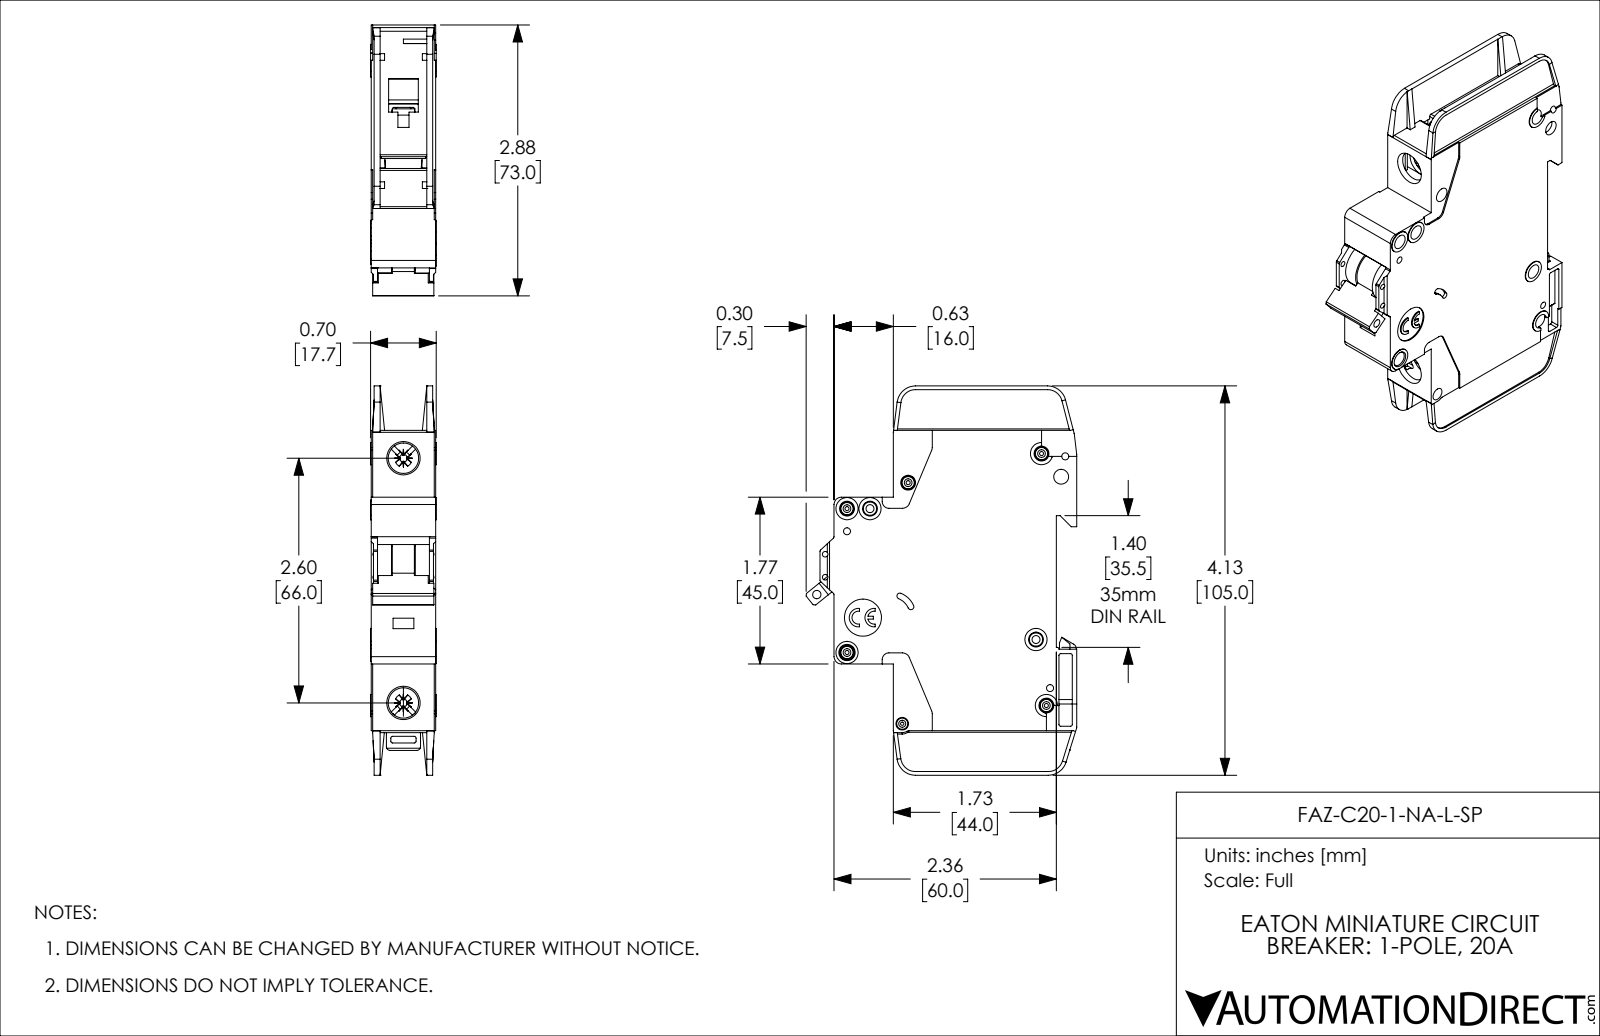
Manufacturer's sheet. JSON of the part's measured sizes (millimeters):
{"part_name": "FAZ-C20-1-NA-L-SP", "step_written_by": "SolidWorks 2019 (AUTOMOTIVE_DESIGN)", "units": "millimeters", "bodies": {"solids": 1, "faces": 1127, "planar": 671, "cylindrical": 357, "other": 99}, "overall_size": [105, 73.1, 17.7], "volume_mm3": 76720, "surface_area_mm2": 26460, "round_holes": [[4, 8], [1.1, 5], [1.9, 4], [1.5, 2], [2.2, 2], [8.2, 2], [0.9, 1], [2.3, 1], [2.5, 1], [3.4, 1], [10, 1]], "round_bosses_or_shafts": [[3.3, 5], [6, 4], [3, 2], [2.5, 1]], "partial_cylinders_radius": [[0.5, 42], [0.4, 10], [1, 10], [2, 8], [5, 5], [0.2, 4], [0.7, 4], [1.1, 4]], "face_to_face_distances": [1.2, 17.4, 15, 16.2, 2.4, 13.8, 0.4, 0.8, 12.6, 14.6], "hole_center_spacings": [6.2, 13.6, 22.1, 4.8, 5.1, 5.2, 5.6, 6.1]}
